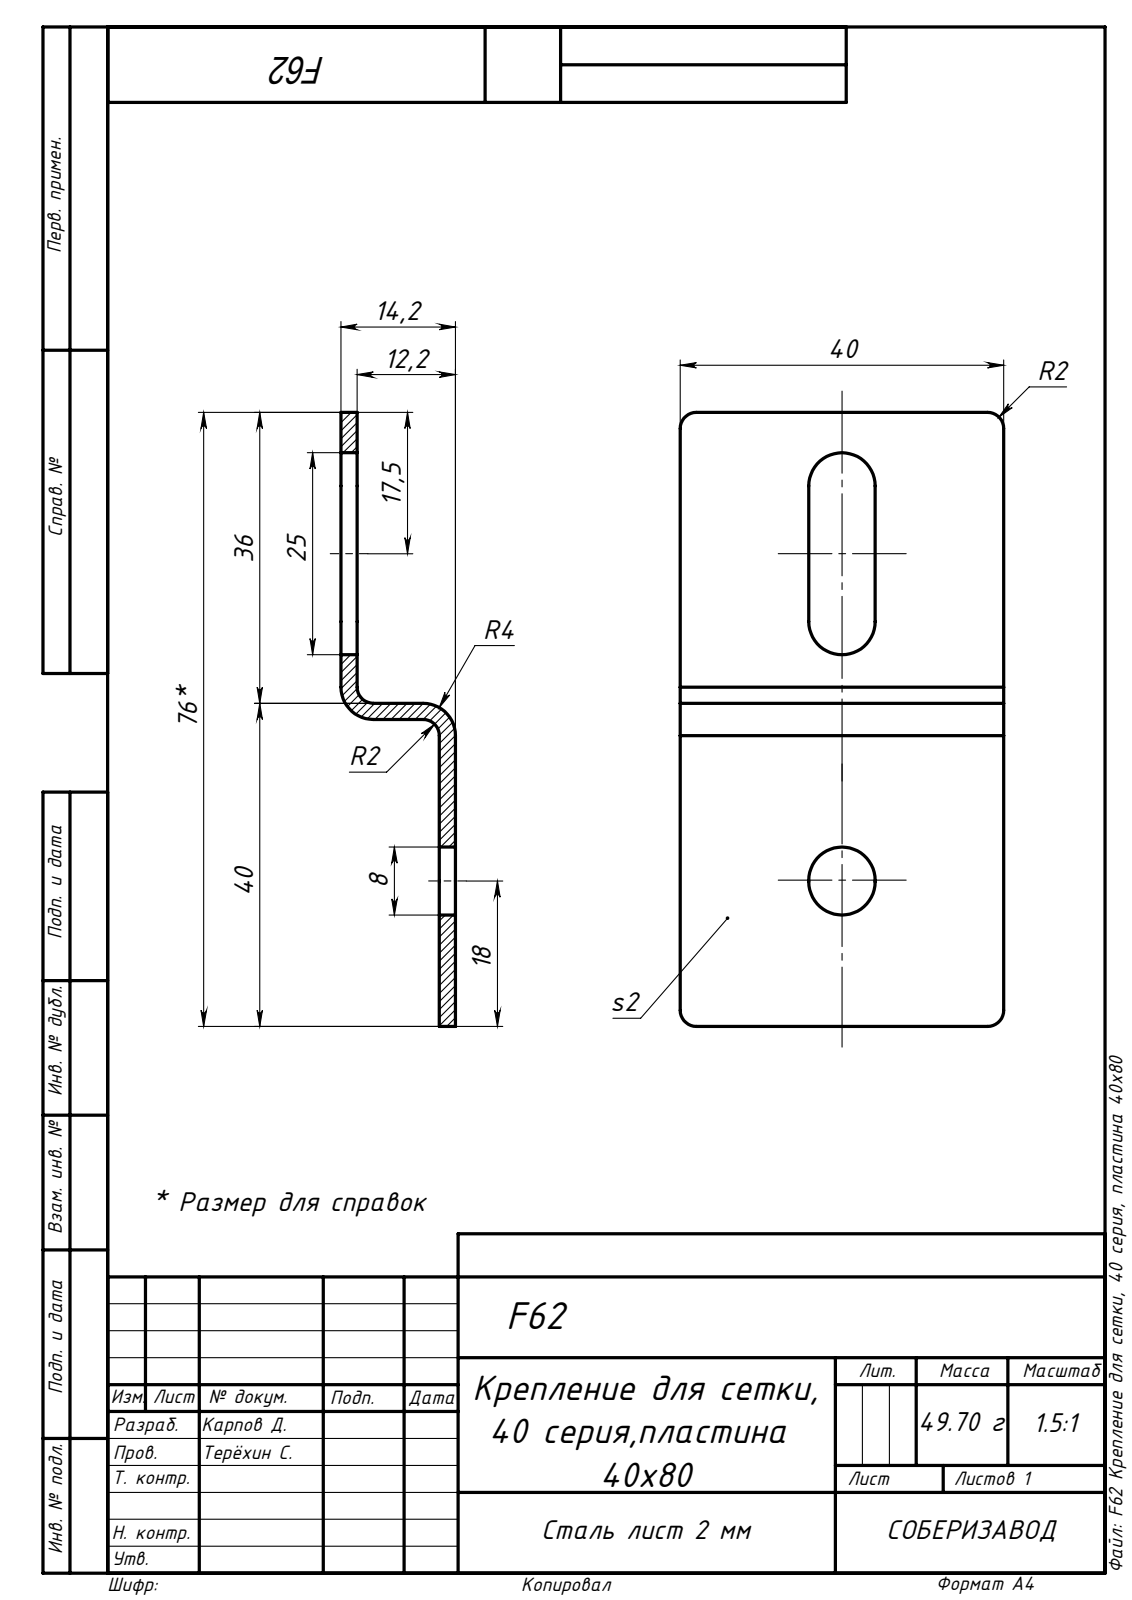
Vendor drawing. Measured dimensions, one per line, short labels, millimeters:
name: F62 Крепление для сетки, 40 серия, пластина 40х80
written by: SolidWorks 2020 (AUTOMOTIVE_DESIGN)
unit: mm
bodies: 1 solid, 36 faces (22 planar, 14 cylindrical, 0 other)
size: 76 × 40 × 14.17
volume: 6 351 mm³; area: 7 017 mm²
rounds: 6× R2, 4× R4.1, 2× R4
face distances: 2, 12.17, 10.17, 14.17, 40, 38, 76, 36, 15.9, 24.1
